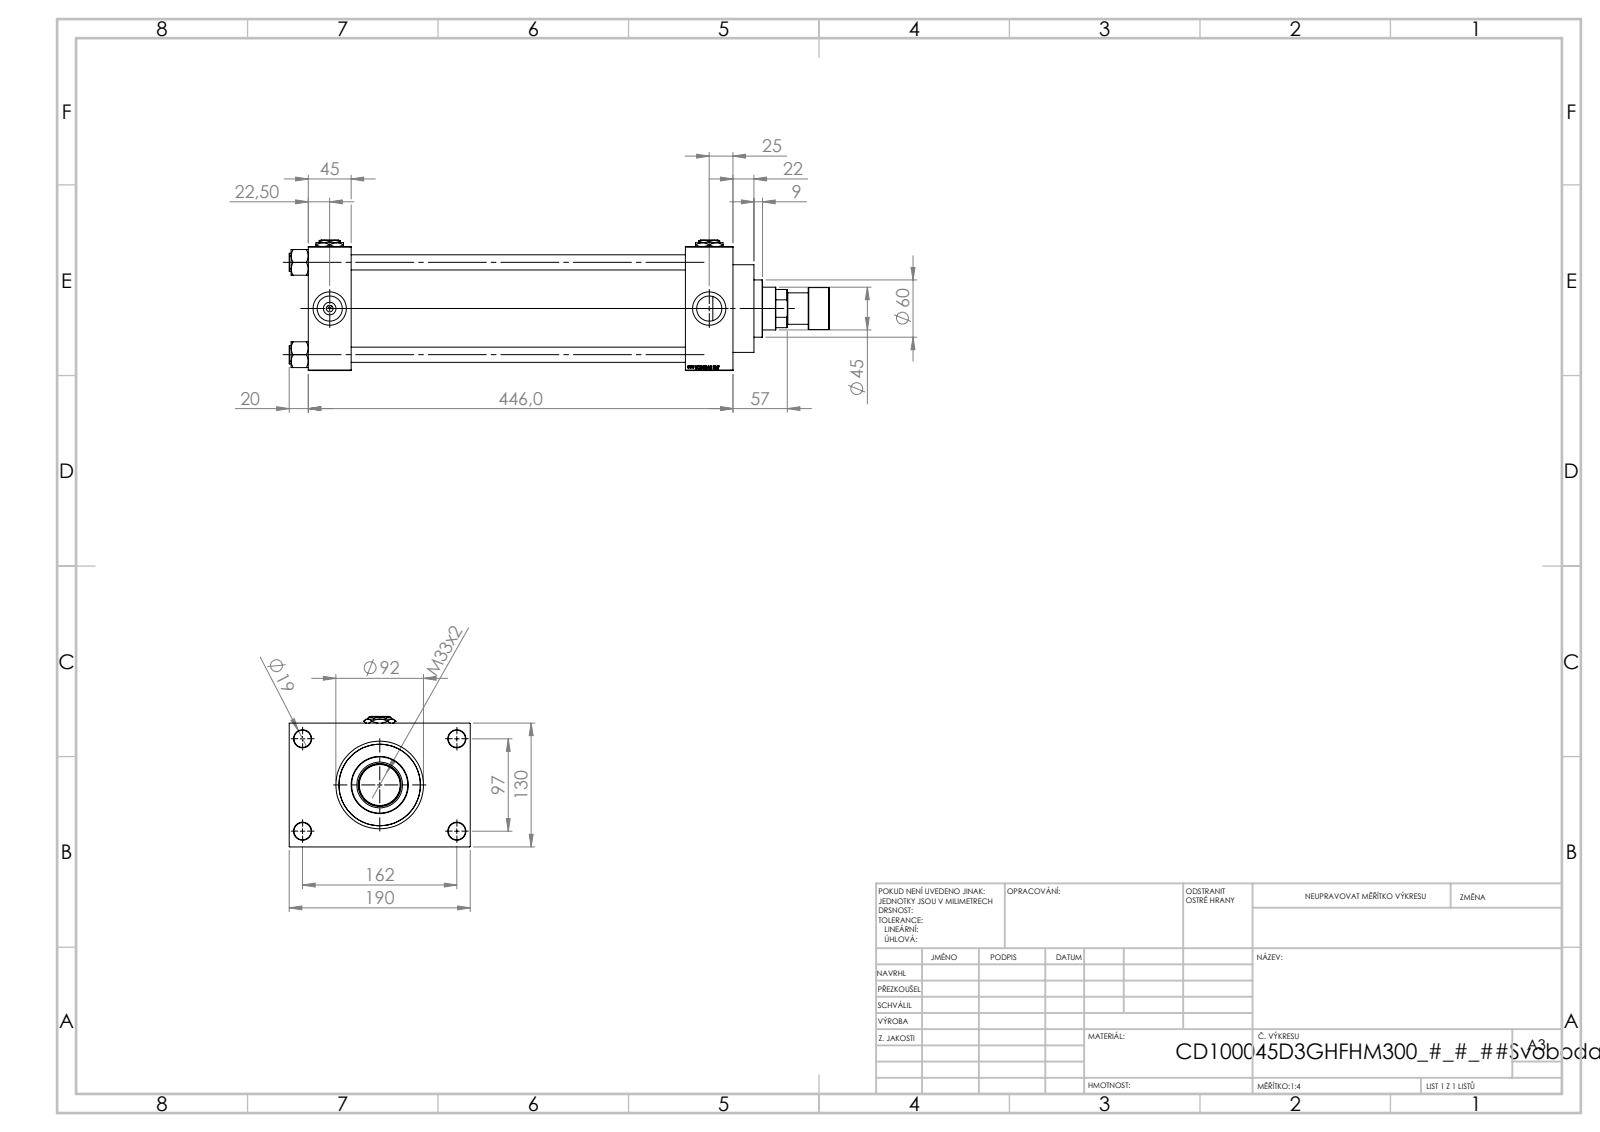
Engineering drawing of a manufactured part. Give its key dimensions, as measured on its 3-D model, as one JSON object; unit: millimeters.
{"part_name": "V215CD_NUT_M5_D; V215CR_ROD_END_F; Zatka_pro_OIL_PORT; V215CD_D_Body (+3 more)", "step_written_by": "SolidWorks 2019 (CONFIG_CONTROL_DESIGN)", "units": "millimeters", "bodies": {"solids": 14, "faces": 1265, "planar": 596, "cylindrical": 103, "other": 566}, "overall_size": [567, 190, 137], "volume_mm3": 3571000, "surface_area_mm2": 647262, "round_holes": [[16, 4], [18, 4], [26.44, 4], [35, 4], [7, 3], [31.5, 1], [45, 1], [48, 1], [76, 1], [85.5, 1], [100, 1]], "round_bosses_or_shafts": [[19, 4], [106, 1], [92, 1], [60, 1], [44, 1], [33, 1]], "face_to_face_distances": [45, 130, 396, 351, 446, 401, 50, 30, 160, 96], "hole_center_spacings": [32.55, 68.52, 94.41, 96.9, 102.27, 129.45, 161.73, 97]}
